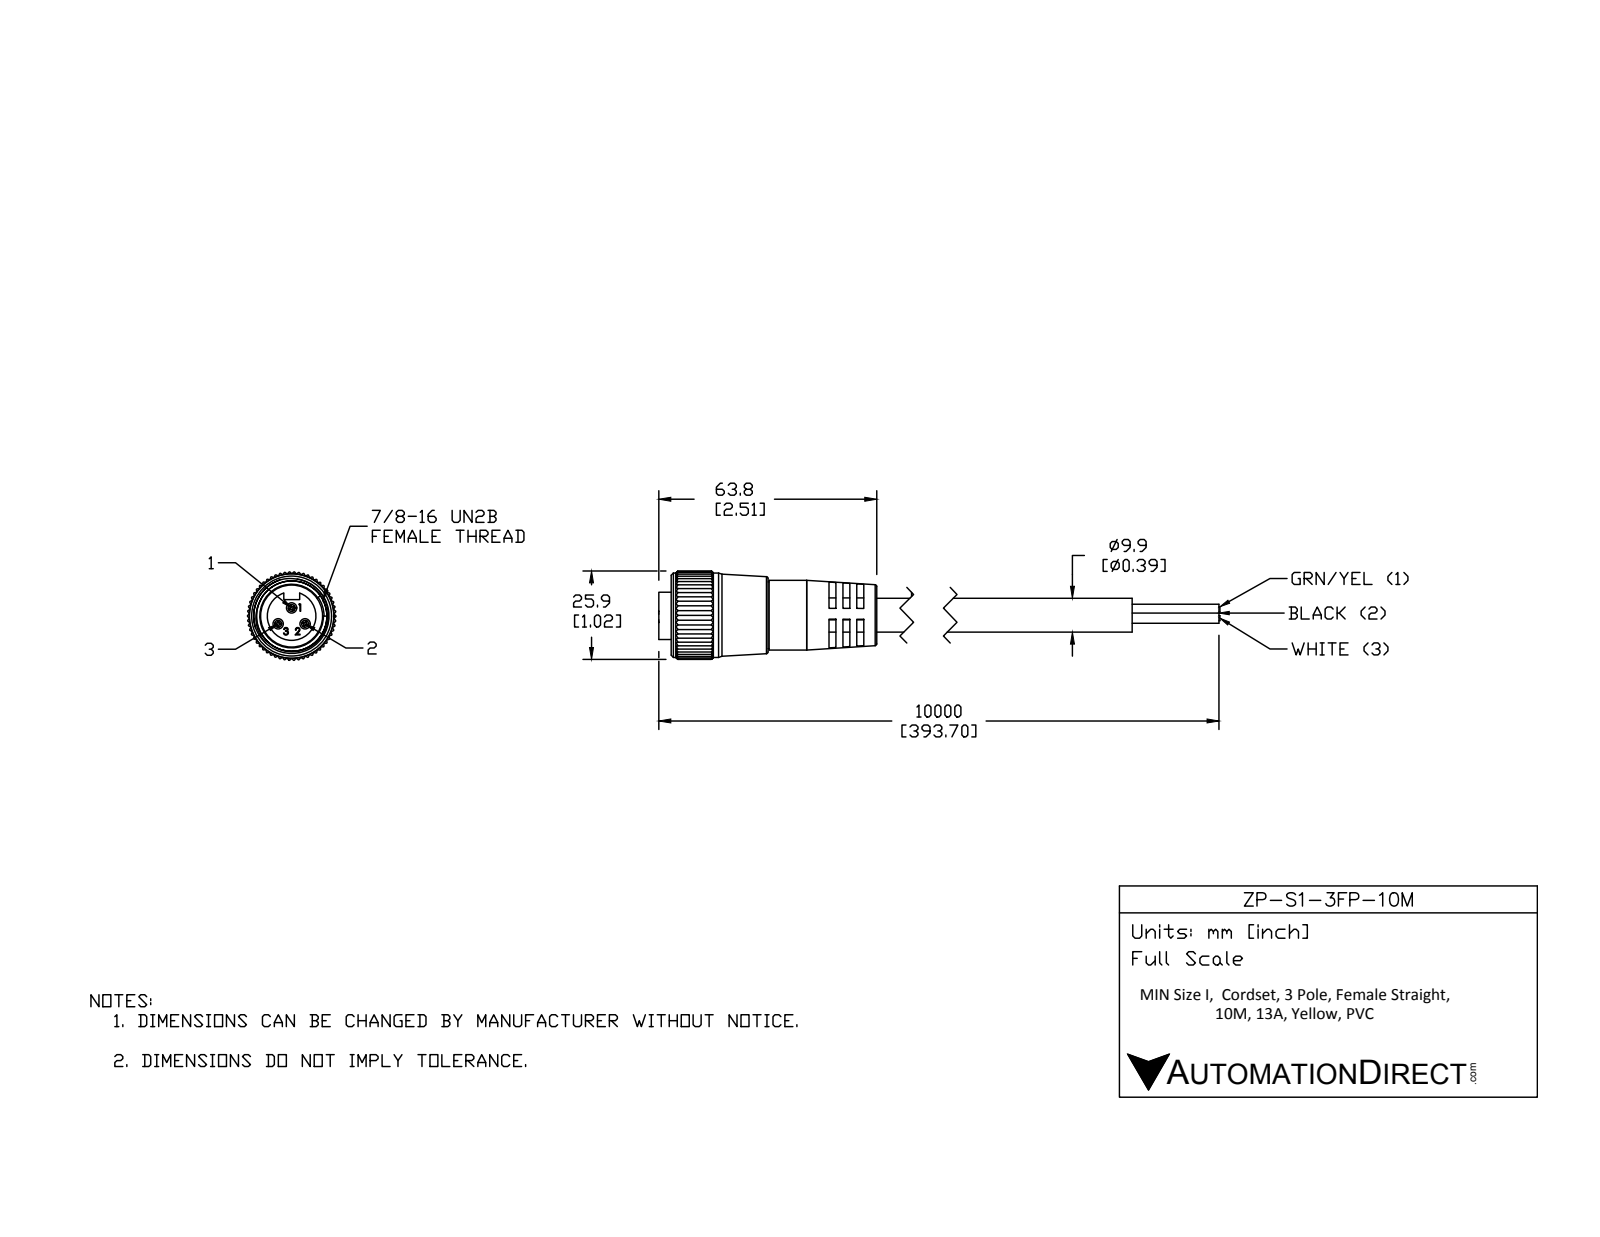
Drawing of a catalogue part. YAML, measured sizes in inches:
part_name: "ZP-S1-3FP-10M"
step_written_by: "SolidWorks 2015 (AUTOMOTIVE_DESIGN)"
units: inches
bodies: {solids: 2, faces: 540, planar: 192, cylindrical: 306, other: 42}
overall_size: [4.28, 2.083, 1.017]
volume: 1.632
surface_area: 18.35
round_holes:
  - {diameter: 0.12, count: 3}
  - {diameter: 0.714, count: 1}
  - {diameter: 0.81, count: 1}
  - {diameter: 0.827, count: 1}
round_bosses_or_shafts:
  - {diameter: 0.39, count: 2}
  - {diameter: 0.972, count: 1}
  - {diameter: 0.803, count: 1}
  - {diameter: 0.768, count: 1}
  - {diameter: 0.56, count: 1}
partial_cylinders:
  - {radius: 0.01, count: 165}
  - {radius: 0.207, count: 1}
  - {radius: 0.509, count: 1}
face_to_face_distances: [0.159, 0.079, 0.08, 0.237, 0.317, 0.546, 0.467, 0.387, 0.309, 0.239]
hole_center_spacings: [0.239, 0.093, 0.178, 0.179, 0.31]
